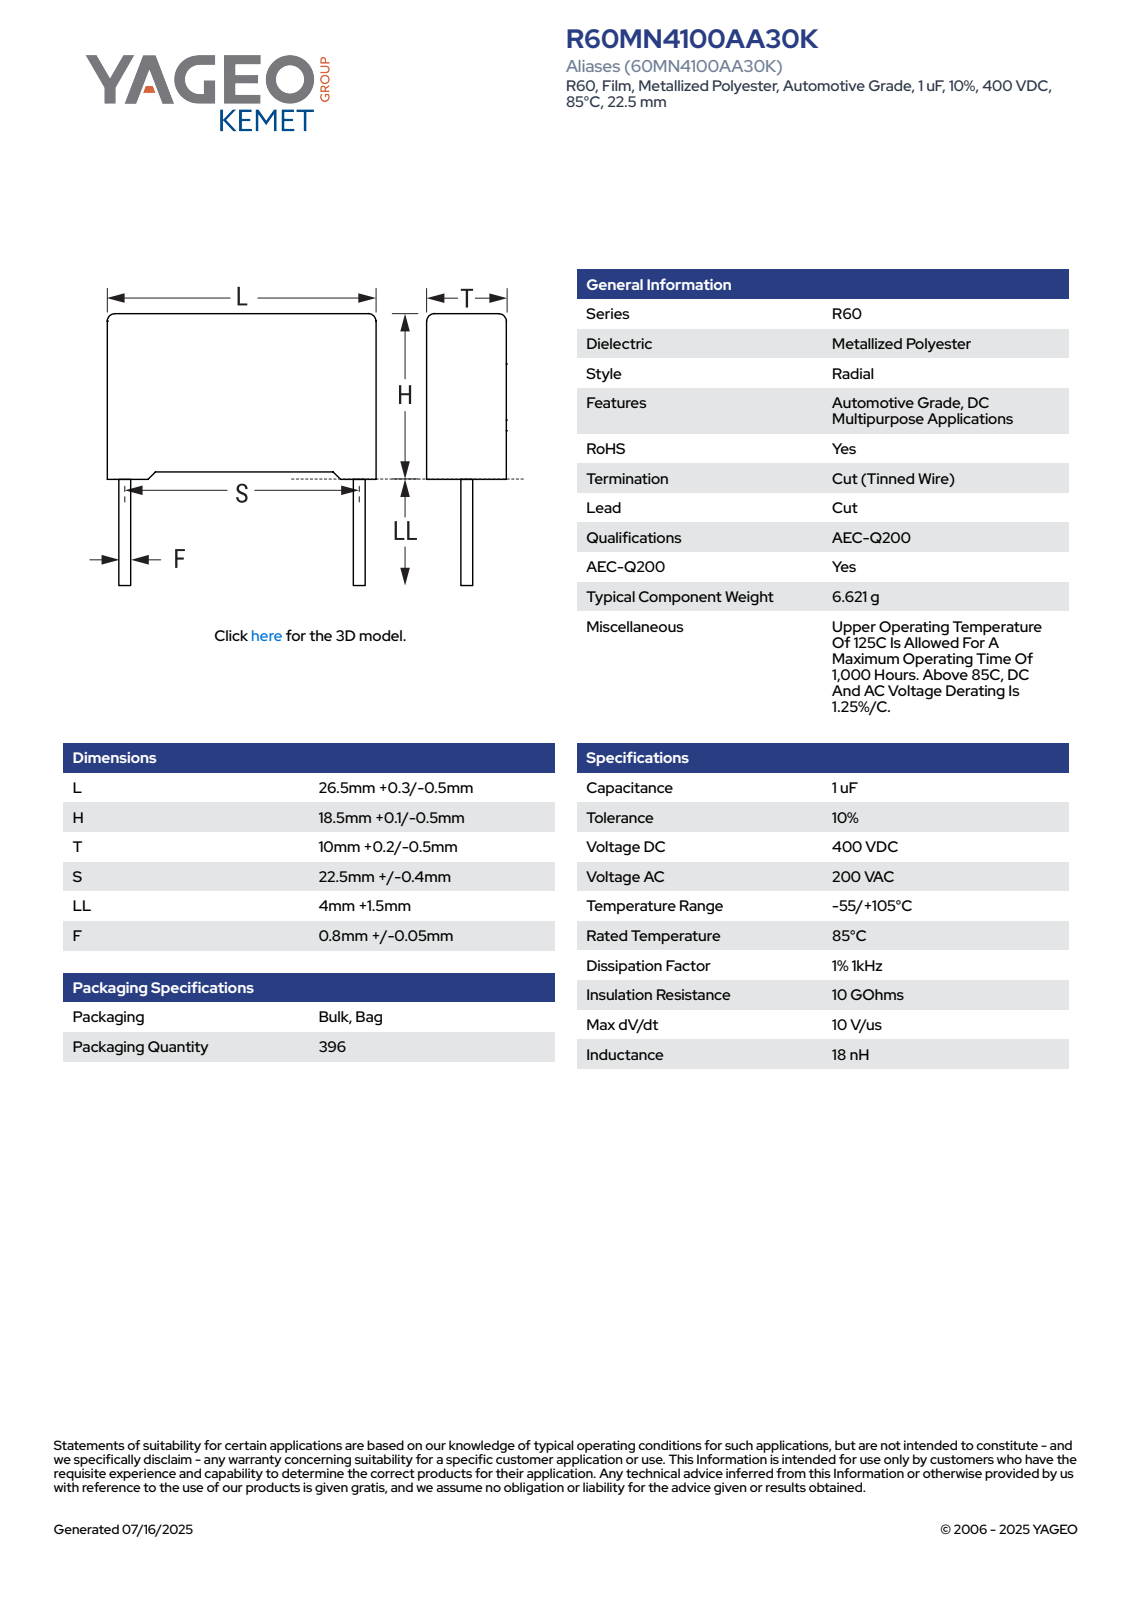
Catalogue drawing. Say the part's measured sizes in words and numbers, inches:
The part is named "CFR_RB2_26.5X18.5X10_L26.8H18.6T10.2S22.5LL5.5F0.85". Its 3-D file was written by "SolidWorks 2021 (AUTOMOTIVE_DESIGN)". It is 4 solids with 85 faces: 77 planar, 8 cylindrical and 0 other. Overall it measures 1.055 by 0.949 by 0.402 inches. Its volume is 0.3 cubic inches and its surface area 3.095 square inches. Round bosses or shafts: 2 of diameter 0.033. Partial cylindrical surfaces (rounded edges, fillets, slot ends): 4 of radius 0.02. The main face-to-face distances are 0.402, 0.703, 1.055, 0.707, 0.03, 0.025, 0.732, 0.035, 0.367, 1.02.
